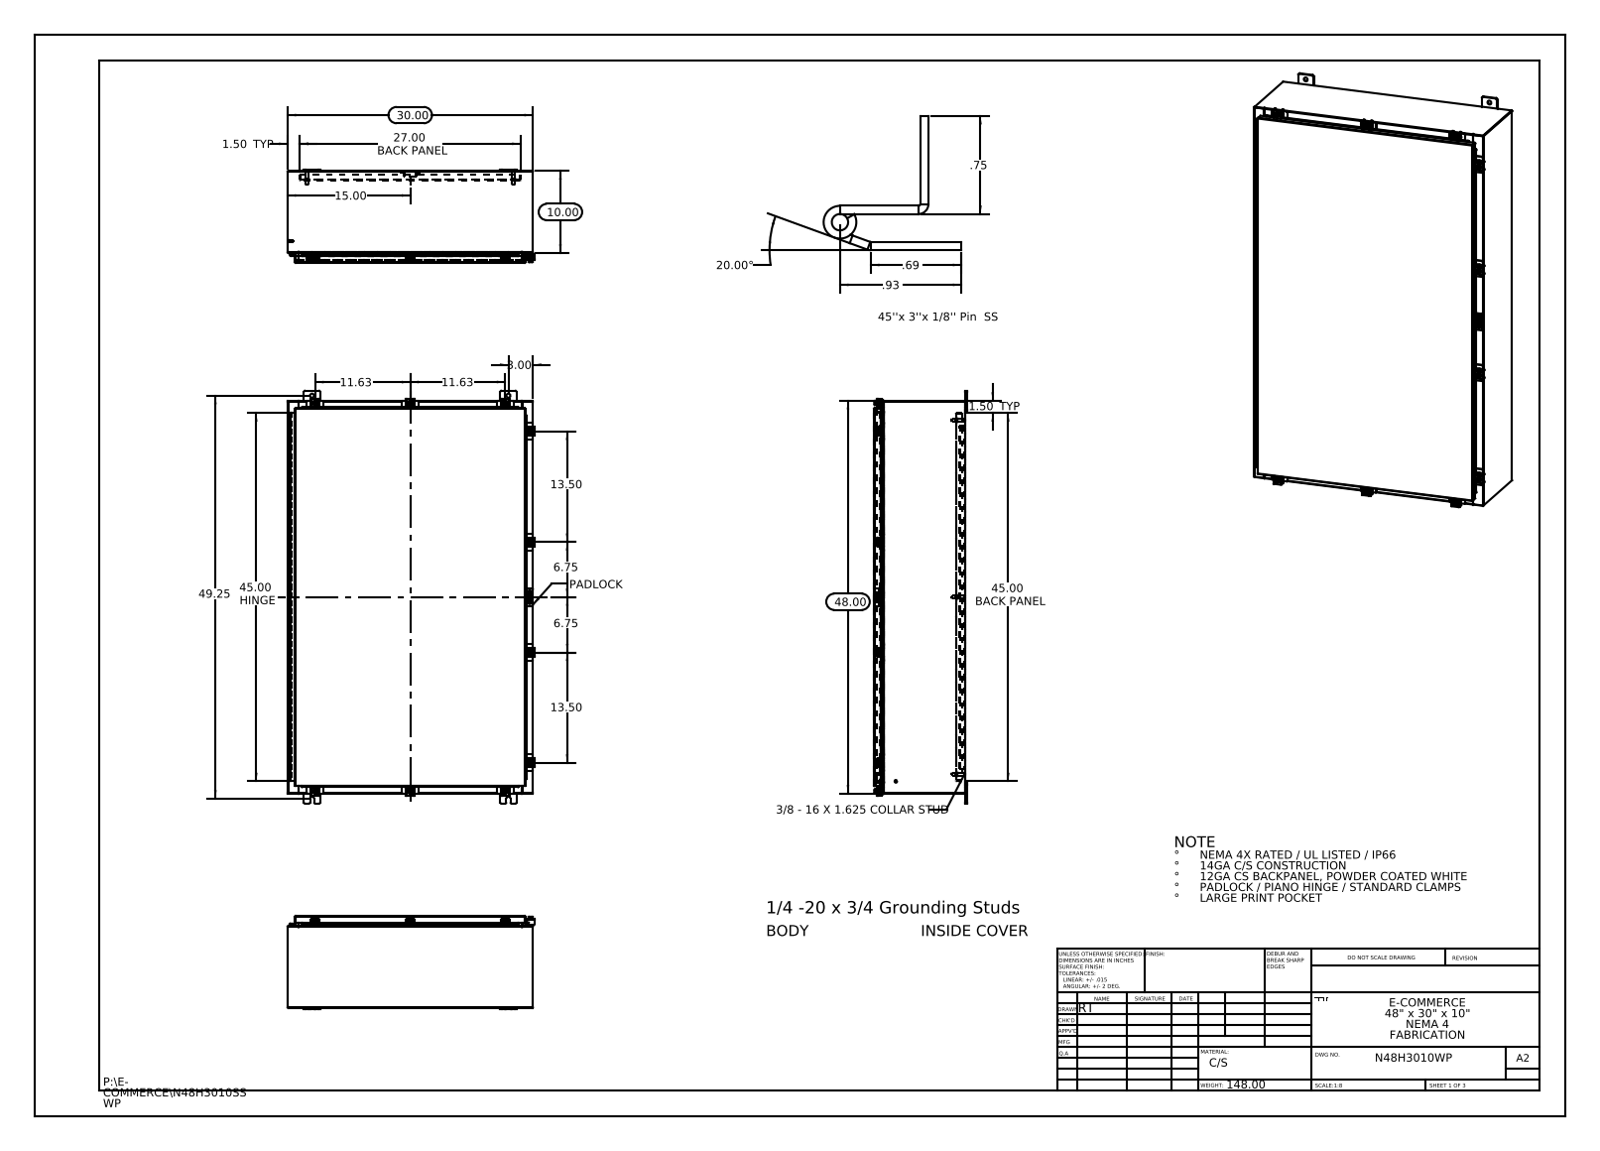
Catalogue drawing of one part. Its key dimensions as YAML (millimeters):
part_name: "N48H3010SSWP 125 Pin Hinge; N48H3010SSWP Padlock Staple; Quarter-20 CD Stud; N48H3010SSWP Mounting Feet (+8 more)"
step_written_by: "SolidWorks 2013 (CONFIG_CONTROL_DESIGN)"
units: millimeters
bodies: {solids: 72, faces: 2887, planar: 1498, cylindrical: 1229, other: 160}
overall_size: [1282.7, 767.4, 289.3]
volume: 8500000
surface_area: 8337000
round_holes:
  - {diameter: 5.4, count: 10}
  - {diameter: 6.6, count: 10}
  - {diameter: 12.7, count: 10}
  - {diameter: 3.2, count: 2}
round_bosses_or_shafts:
  - {diameter: 6.4, count: 11}
  - {diameter: 12.7, count: 10}
  - {diameter: 10.1, count: 10}
  - {diameter: 15.9, count: 6}
  - {diameter: 9.5, count: 6}
  - {diameter: 8.4, count: 6}
  - {diameter: 8, count: 2}
  - {diameter: 6, count: 2}
partial_cylinders:
  - {radius: 1.5, count: 46}
  - {radius: 0.3, count: 31}
  - {radius: 2.2, count: 25}
  - {radius: 4.8, count: 24}
  - {radius: 3, count: 20}
  - {radius: 3.6, count: 20}
  - {radius: 1.3, count: 15}
  - {radius: 2, count: 14}
face_to_face_distances: [1.9, 282.6, 280.7, 2.6, 284.5, 25.4, 257.2, 27.3, 255.3, 29.9]
hole_center_spacings: [549.3, 682.7, 844.4, 1152.2, 1195.7, 1240.9, 342.9, 641.4]
